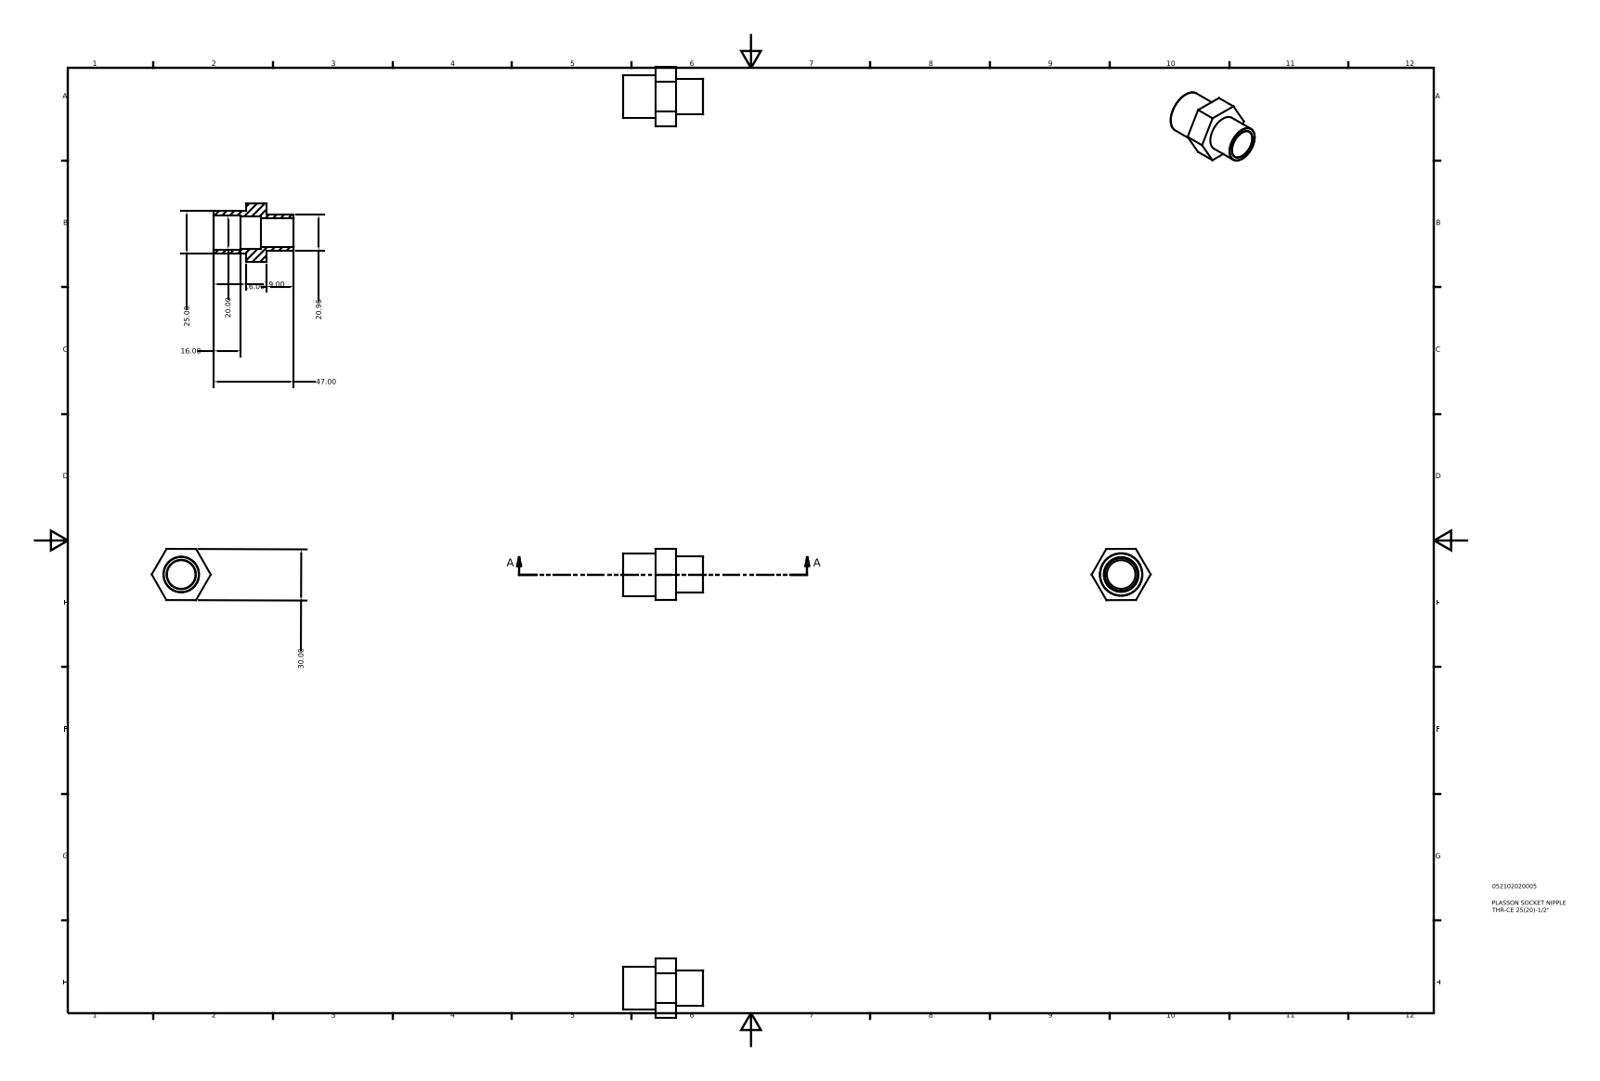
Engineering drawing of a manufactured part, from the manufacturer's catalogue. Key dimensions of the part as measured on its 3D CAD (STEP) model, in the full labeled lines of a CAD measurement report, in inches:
Part name (STEP PRODUCT): 052102020005
STEP written by: Autodesk Inventor 2015 (AUTOMOTIVE_DESIGN)
Units: inches
Bodies: 1 solid, 21 faces (12 planar, 5 cylindrical, 4 other)
Overall size (bounding box): 1.85 × 1.364 × 1.183
Volume: 0.707 in³ · Surface area: 11.79 in²
Round holes (diameter × count): ⌀0.66 ×1, ⌀0.748 ×1, ⌀0.787 ×1
Round bosses / shafts (diameter × count): ⌀0.984 ×1, ⌀0.825 ×1
Main face-to-face distances: 1.181, 0.472, 1.22, 0.748, 0.63, 1.85, 1.102, 1.094, 0.346, 0.126
